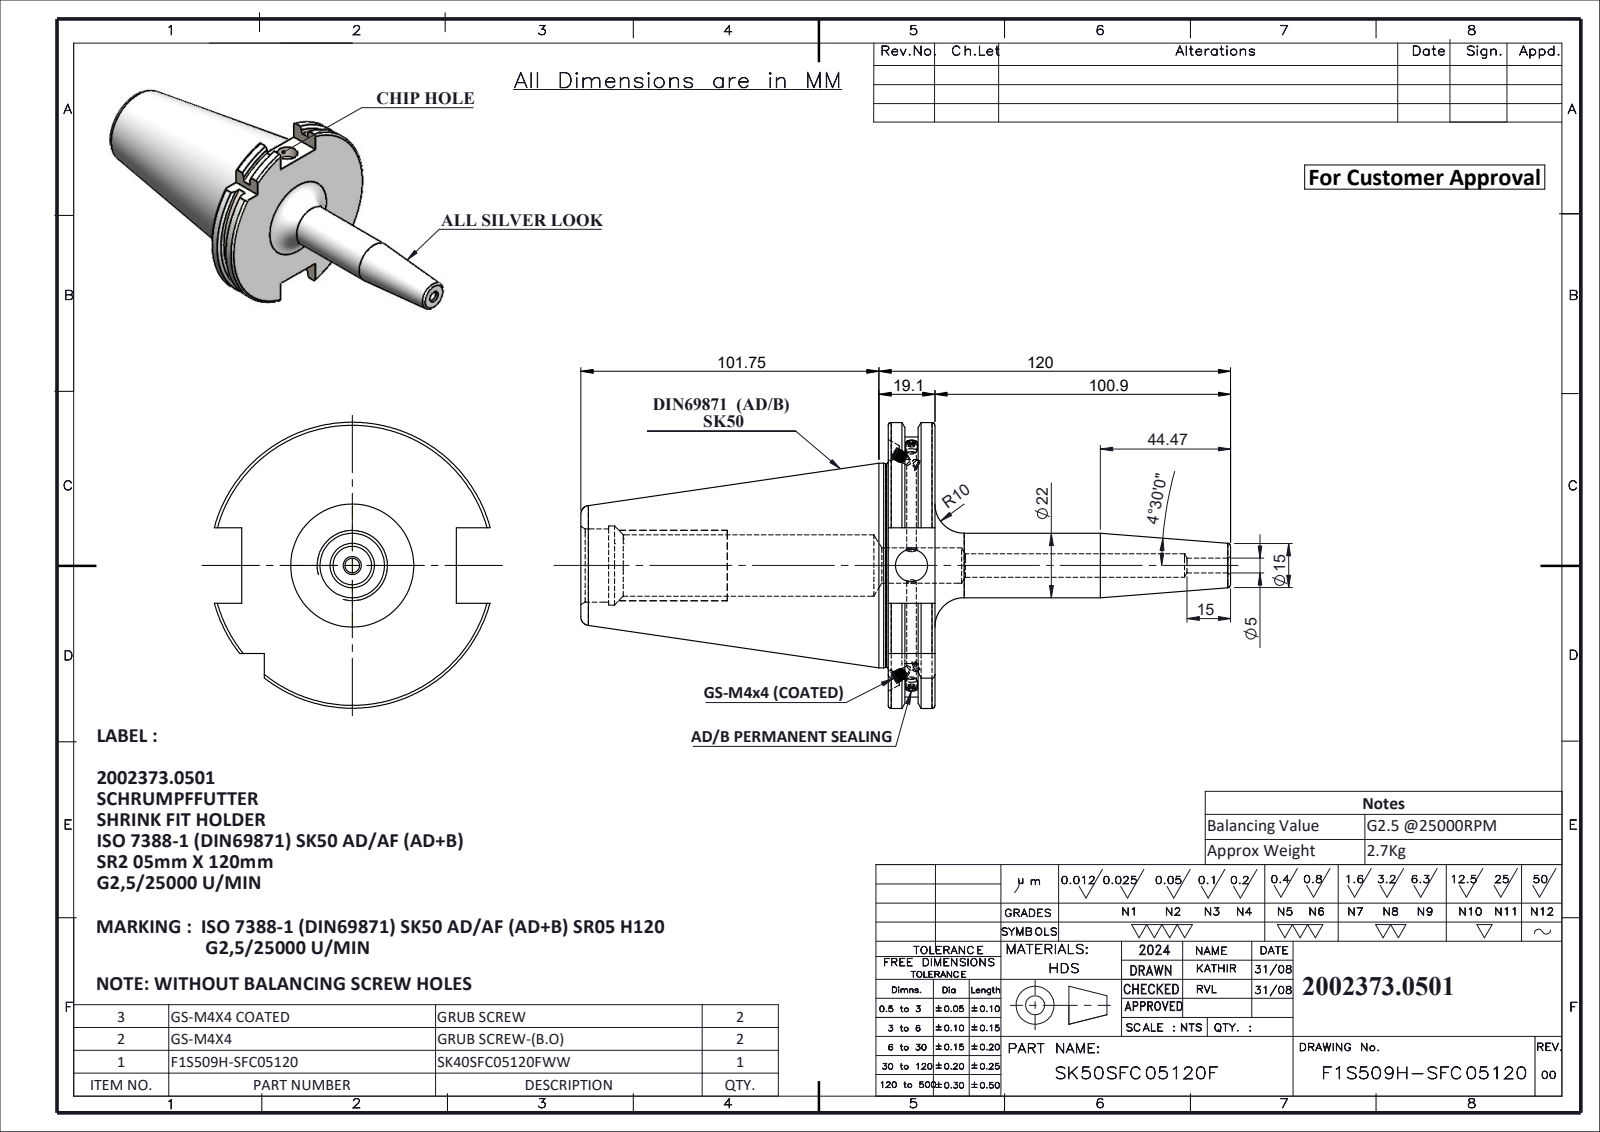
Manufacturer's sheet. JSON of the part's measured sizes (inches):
{"part_name": "GS-M4X4-COATING_DIN 913 - M4 x 4-N; F1S509H-SFC05120; GS-M4X4_DIN 913 - M4 x 4-N; SK50SFC05120FWW", "step_written_by": "SolidWorks 2024 (CONFIG_CONTROL_DESIGN)", "units": "inches", "bodies": {"solids": 5, "faces": 252, "planar": 61, "cylindrical": 75, "other": 116}, "overall_size": [8.73, 3.839, 3.703], "volume_in3": 21.52, "surface_area_in2": 83.23, "round_holes": [[0.126, 2], [0.236, 2], [0.13, 1], [0.197, 1], [0.315, 1], [0.433, 1], [0.472, 1], [0.827, 1], [0.984, 1], [1.063, 1]], "round_bosses_or_shafts": [[0.157, 4], [0.114, 2], [2.75, 1], [2.734, 1], [0.866, 1]], "partial_cylinders_radius": [[1.768, 1], [1.919, 1]], "face_to_face_distances": [0.626, 0.222, 0.404, 0.399, 0.177, 0.227, 4.132, 4.354, 4.531, 4.758]}
